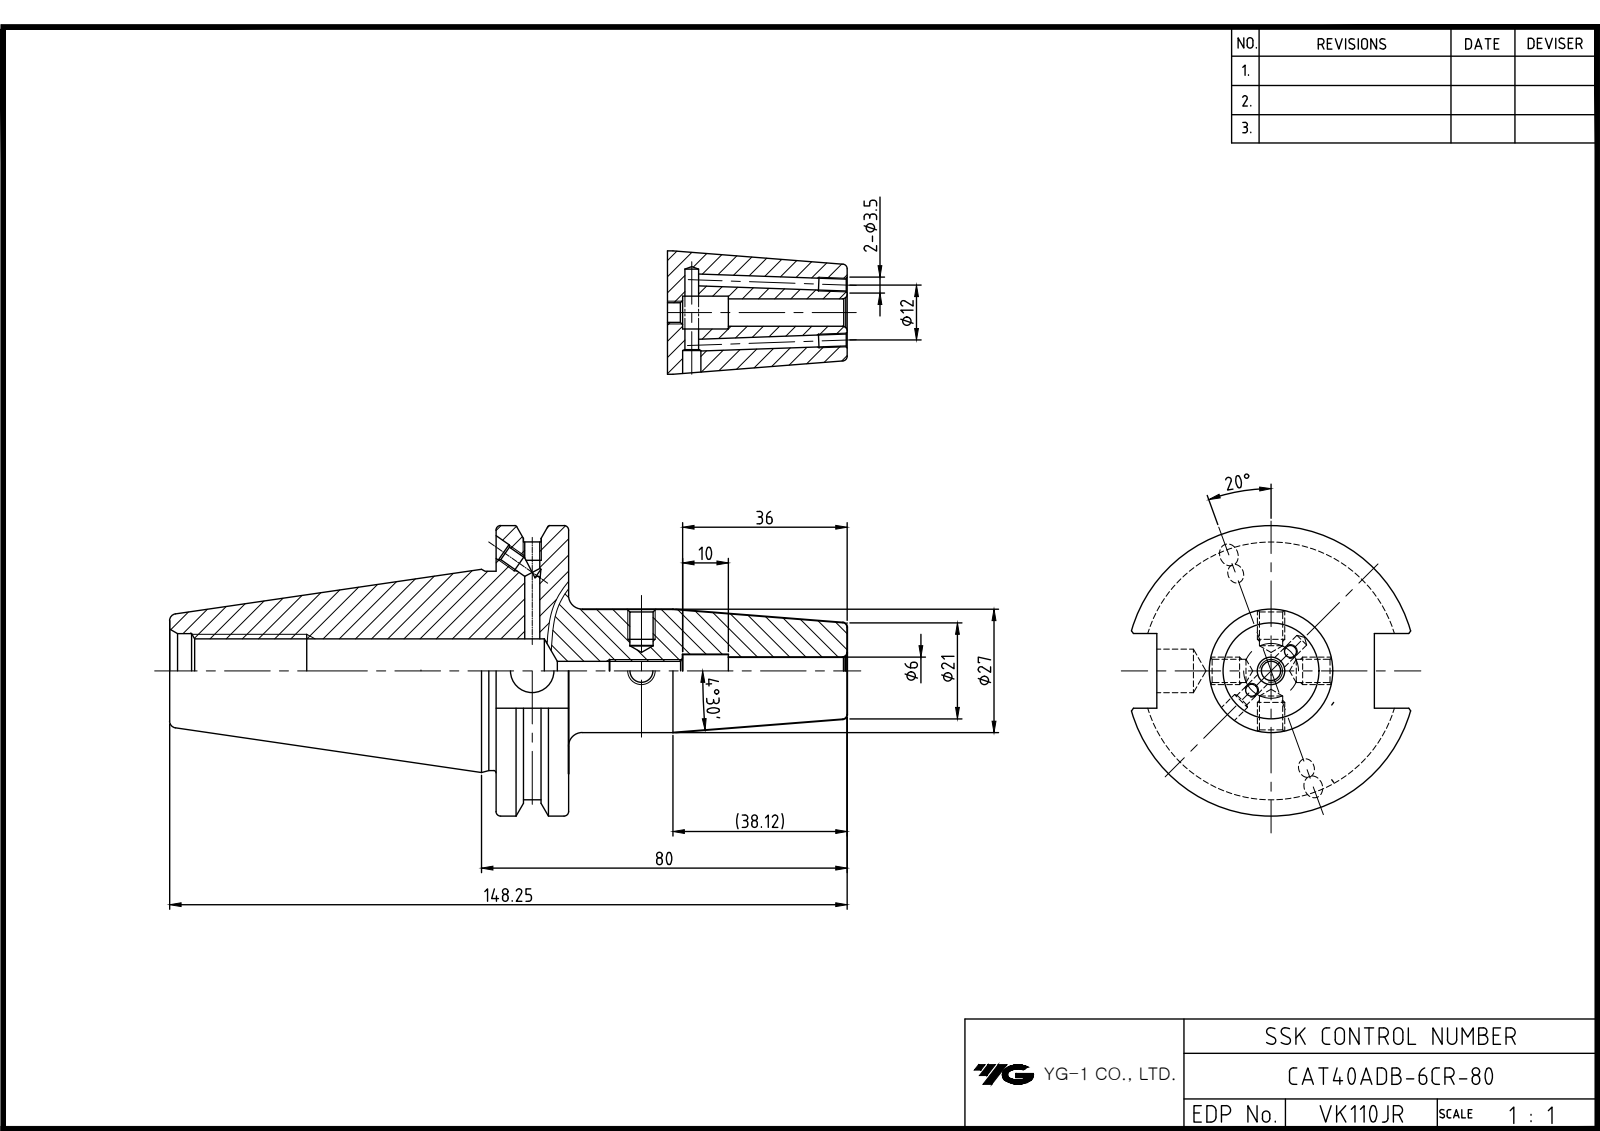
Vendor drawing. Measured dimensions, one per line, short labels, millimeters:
name: LO-CAT40ADB-SFH6CR-80
written by: Autodesk Inventor 2025 (AUTOMOTIVE_DESIGN)
unit: mm
bodies: 1 solid, 90 faces (37 planar, 30 cylindrical, 23 other)
size: 148.25 × 63.5 × 61.09
volume: 129 696 mm³; area: 26 820 mm²
holes: 4× ⌀3.24, 2× ⌀2.46, 2× ⌀4, 2× ⌀4.2, 1× ⌀4.3, 1× ⌀6, 1× ⌀7.2, 1× ⌀9.53, 1× ⌀13.39, 1× ⌀16.3
bosses: 1× ⌀63.5, 1× ⌀43.6, 1× ⌀27
rounds: 1× R28.15
face distances: 15.88, 76.83, 60.95, 47.6, 16.38, 71.42, 87.3, 148.25, 77.47, 6.05
